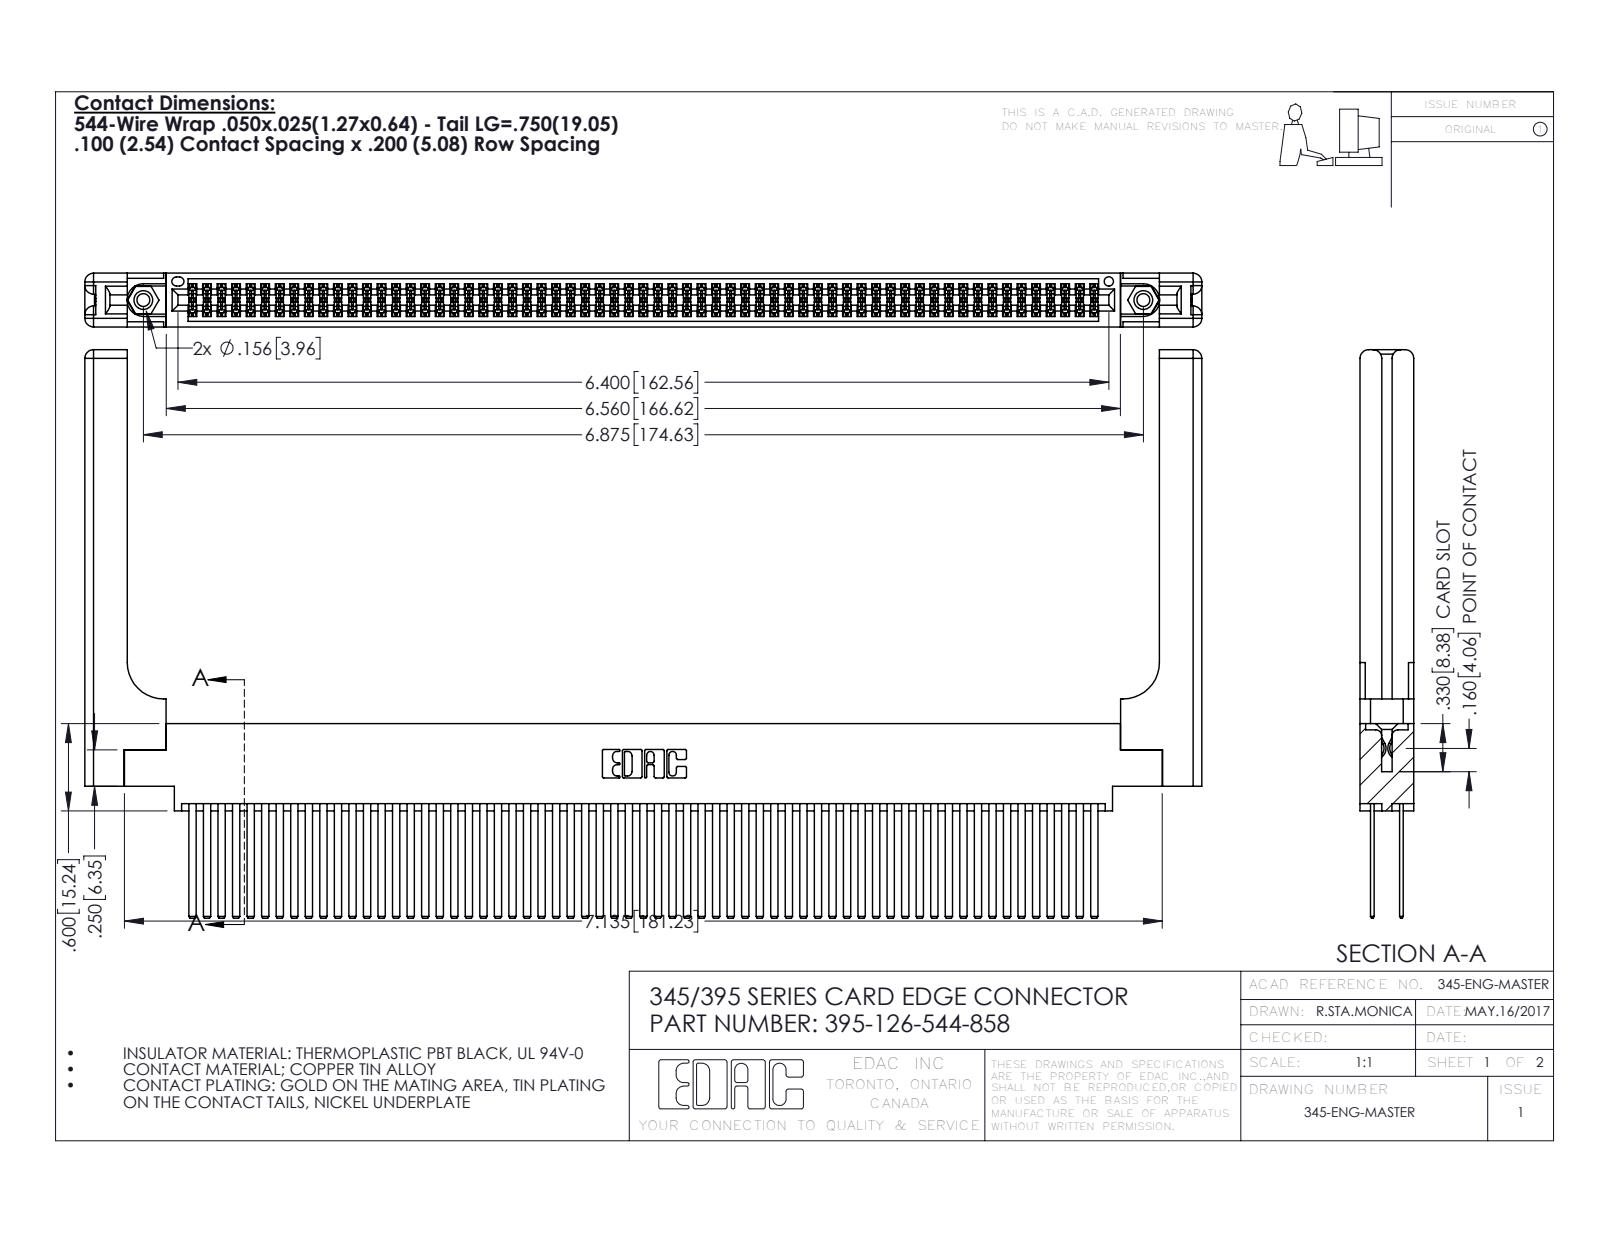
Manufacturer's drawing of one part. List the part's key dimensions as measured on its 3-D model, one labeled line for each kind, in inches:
Part name (STEP PRODUCT): 345-250-001_345-250-001-102; 345-220-058_345-220-058; 345 Part_0.170 Offset - 0.156 Dia-TH; 395-126-544-858 (+1 more)
STEP written by: SolidWorks 2016 (CONFIG_CONTROL_DESIGN)
Units: inches
Bodies: 131 solids, 5930 faces (3886 planar, 1984 cylindrical, 60 other)
Overall size (bounding box): 7.679 × 3.907 × 0.37
Volume: 1.786 in³ · Surface area: 64.36 in²
Round holes (diameter × count): ⌀0.089 ×2, ⌀0.125 ×2, ⌀0.156 ×2, ⌀0.064 ×1
Round bosses / shafts (diameter × count): ⌀0.155 ×2
Partial cylindrical surfaces — rounded edges, fillets, slot ends (radius × count): R0.006 ×189, R0.01 ×22, R0.06 ×16, R0.007 ×6, R0.031 ×6, R0.026 ×3, R0.014 ×2, R0.019 ×2
Main face-to-face distances: 0.072, 0.298, 0.098, 0.272, 0.025, 0.2, 0.37, 0.225, 0.175, 0.148
Hole centre spacings: 0.27, 6.639, 6.875
